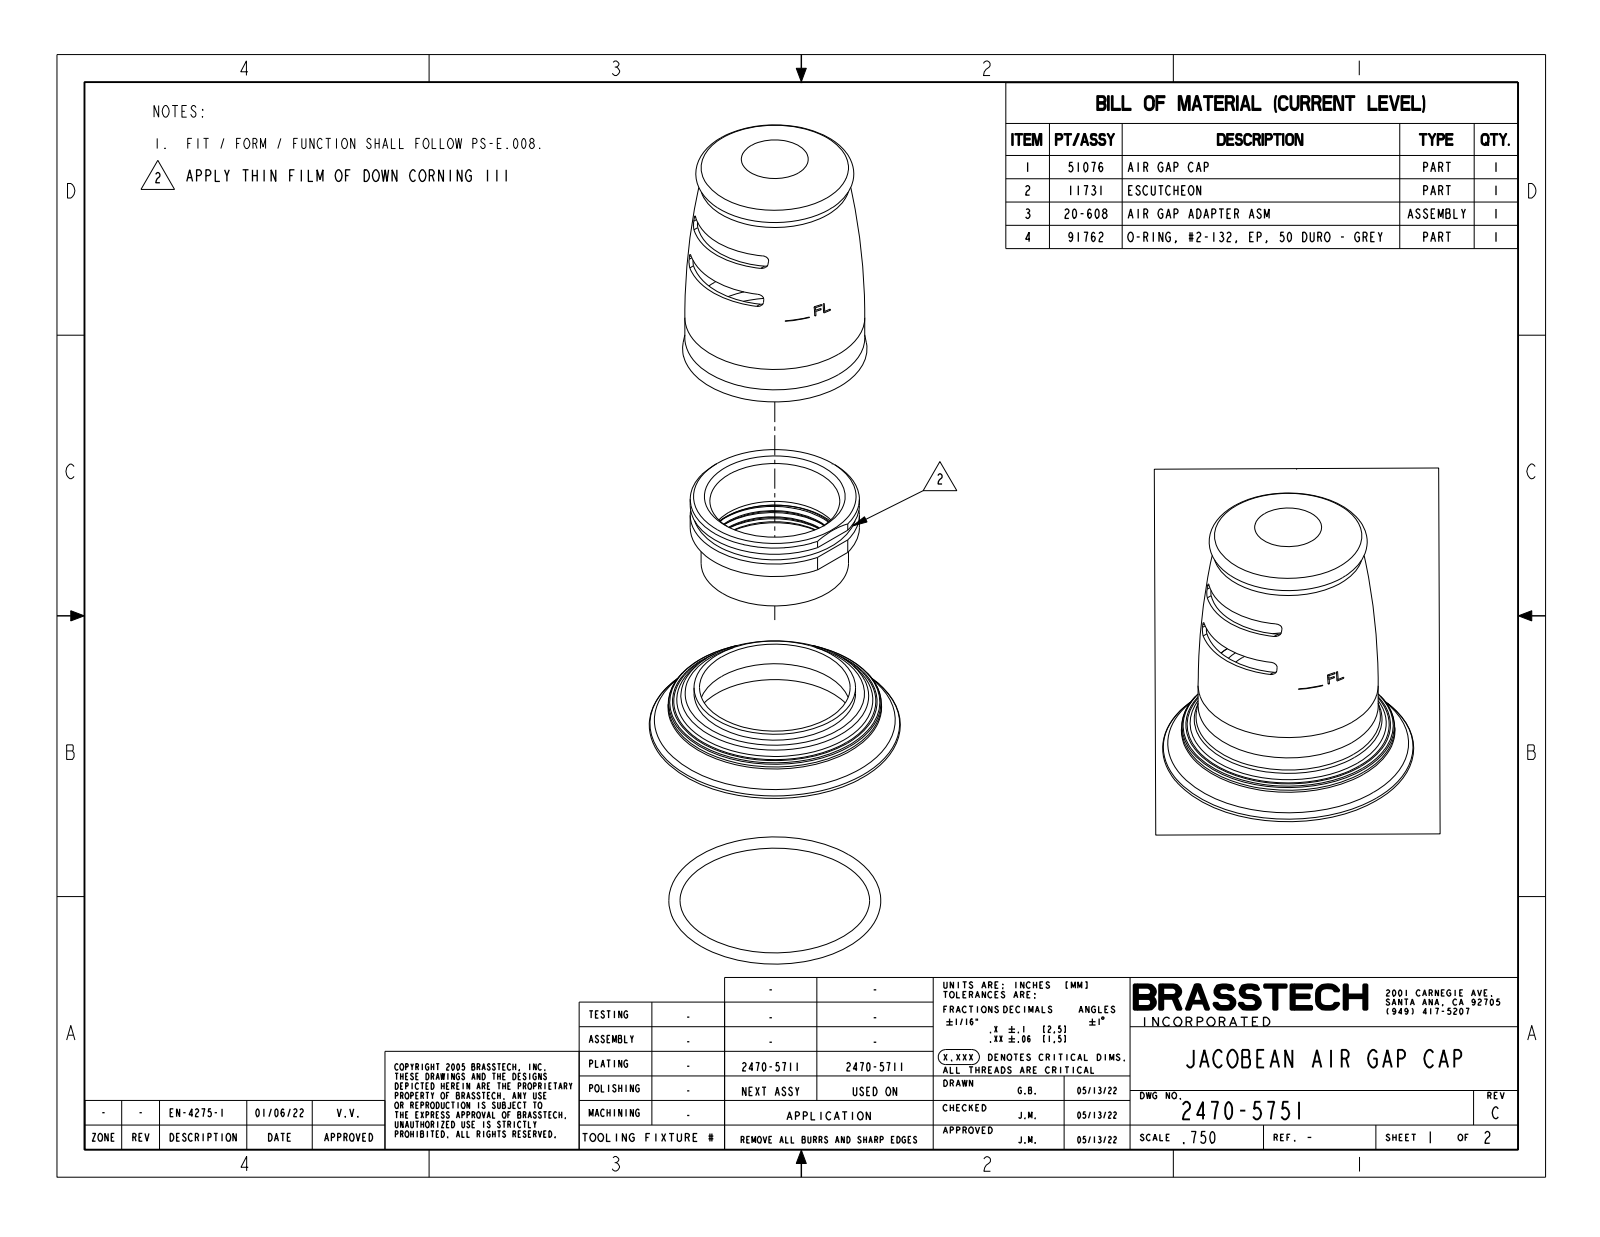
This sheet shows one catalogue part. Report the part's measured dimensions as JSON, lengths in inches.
{"part_name": "50932; 2470-5751_ASM", "step_written_by": "PRO/ENGINEER BY PARAMETRIC TECHNOLOGY CORPORATION, 2013150 (CONFIG_CONTROL_DESIGN)", "units": "inches", "bodies": {"solids": 1, "faces": 120, "planar": 38, "cylindrical": 22, "other": 60}, "overall_size": [2.6, 2, 2], "volume_in3": 0.556, "surface_area_in2": 43.08, "round_holes": [[1.57, 1]], "round_bosses_or_shafts": [[1.65, 1]], "partial_cylinders_radius": [[0.049, 5], [0.05, 3]], "face_to_face_distances": [0.129, 0.4, 1.98, 1.851, 1.579, 0.272, 1.45, 0.529, 0.013, 1.3]}
